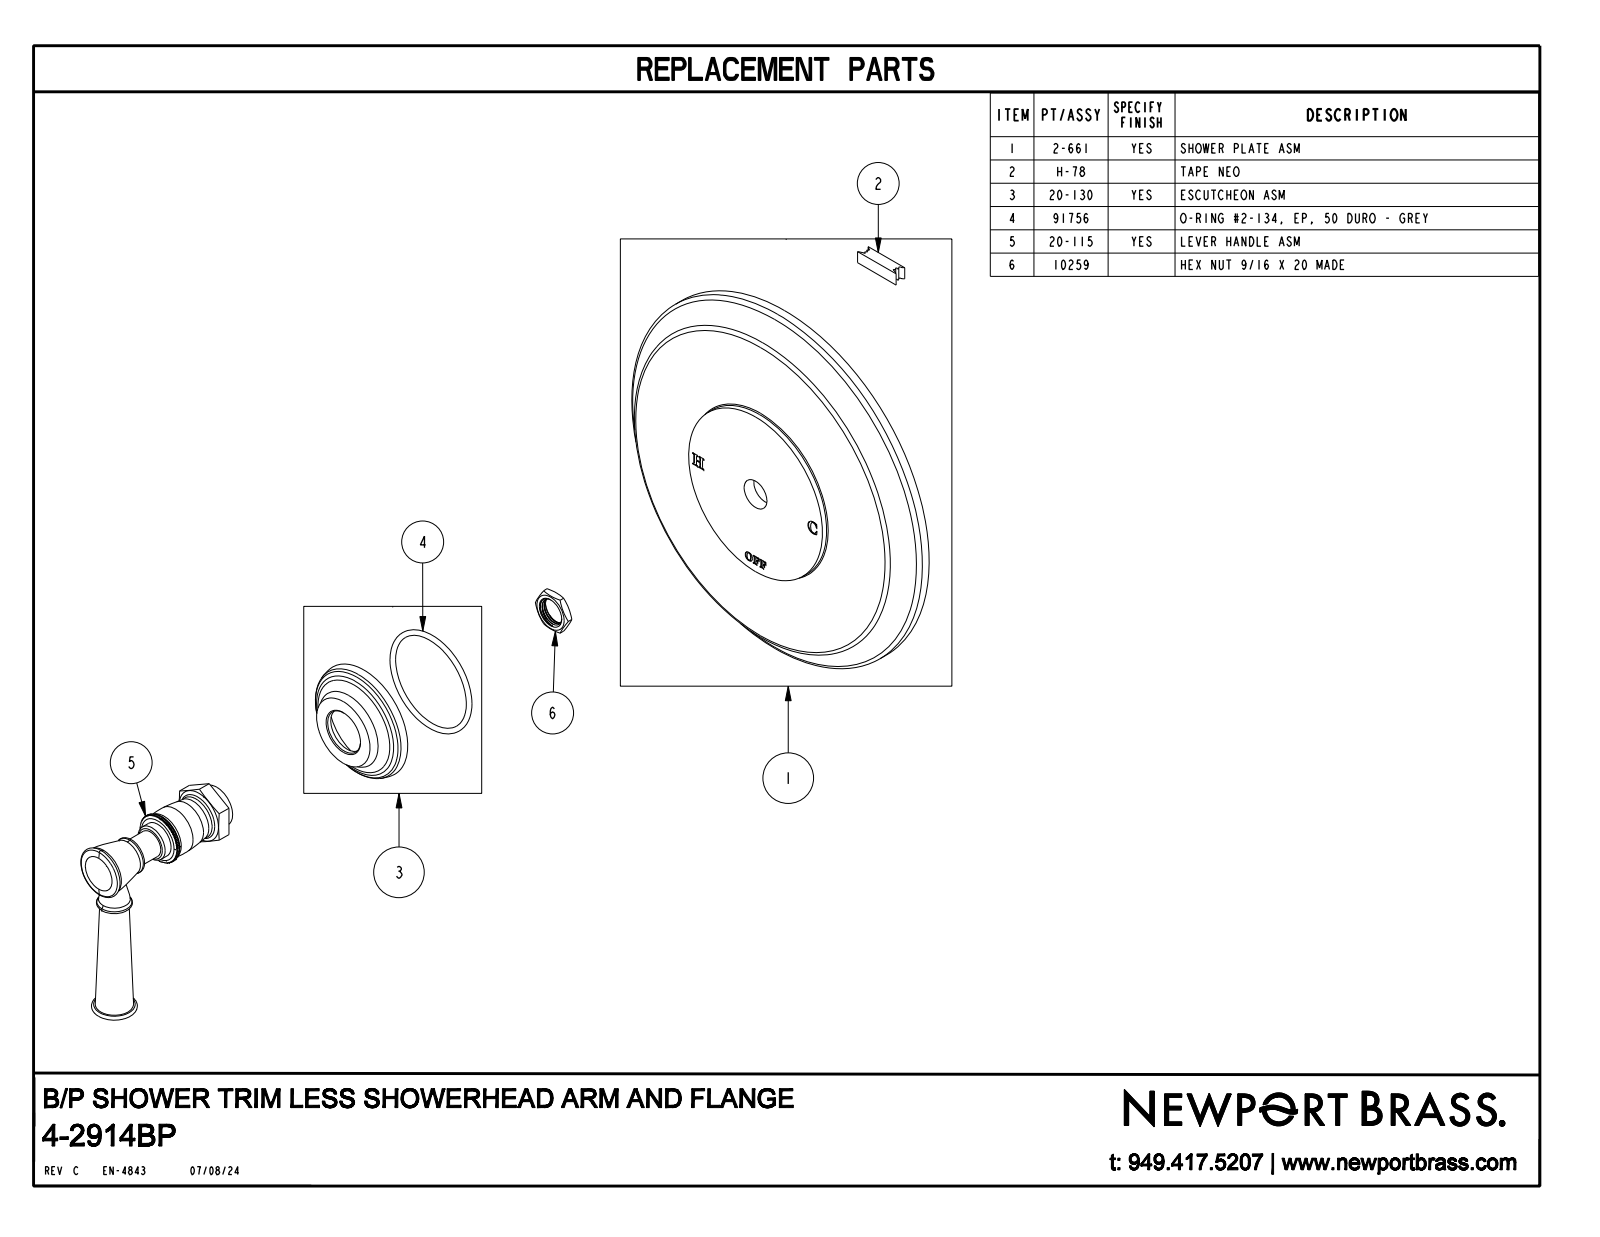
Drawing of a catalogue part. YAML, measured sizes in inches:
part_name: "4-2914BP"
step_written_by: "CREO PARAMETRIC BY PTC INC, 2018400 (CONFIG_CONTROL_DESIGN)"
units: inches
bodies: {solids: 1, faces: 492, planar: 227, cylindrical: 6, other: 259}
overall_size: [7.5, 7.5, 4.169]
volume: 29.7
surface_area: 114.4
round_bosses_or_shafts:
  - {diameter: 7.5, count: 1}
  - {diameter: 0.686, count: 1}
  - {diameter: 0.53, count: 1}
face_to_face_distances: [0.625, 0.75, 0.125, 1.284, 0.659, 0.534, 1.025, 2.614, 1.989, 1.864]
